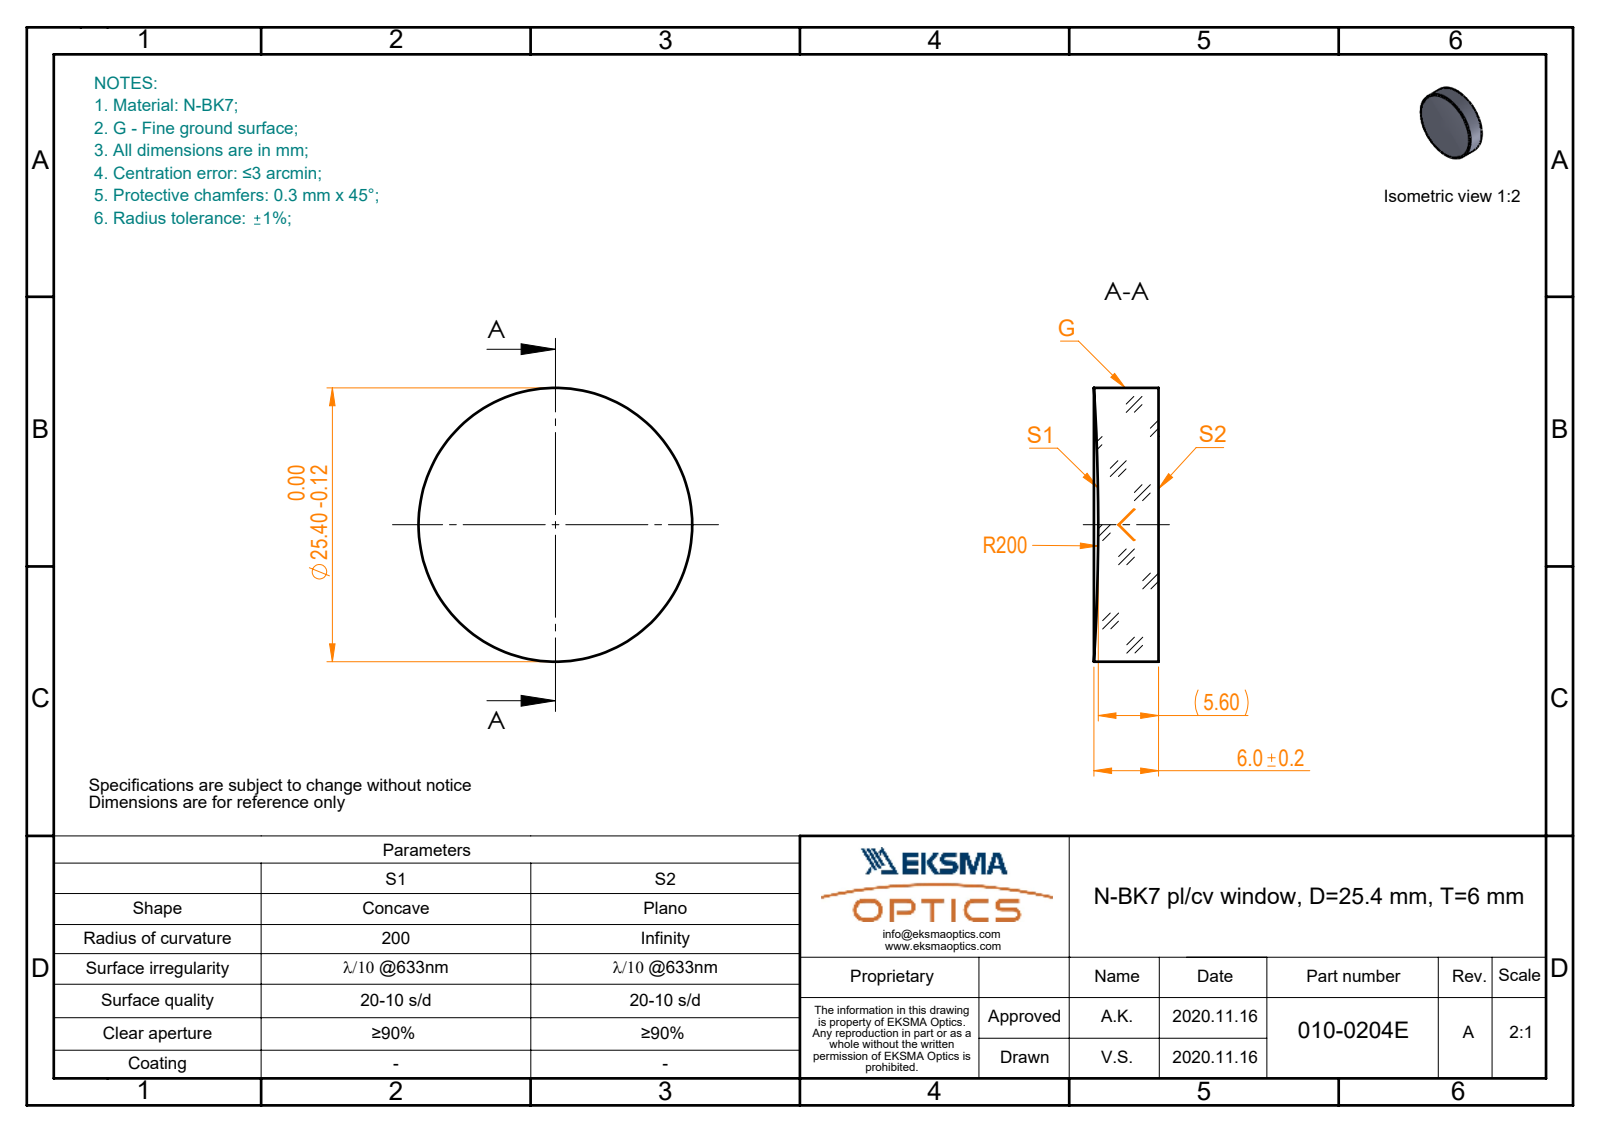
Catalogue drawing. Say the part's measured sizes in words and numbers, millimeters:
The part is named "010-0204E_N-BK7_PCV_window". Its 3-D file was written by "SolidWorks 2019 (CONFIG_CONTROL_DESIGN)". It is 1 solid with 5 faces: 1 planar, 2 cylindrical and 2 other. Overall it measures 25.4 by 25.4 by 6 millimeters. Its volume is 2 938 cubic millimeters and its surface area 1 493 square millimeters. Round bosses or shafts: 1 of diameter 25.4.
